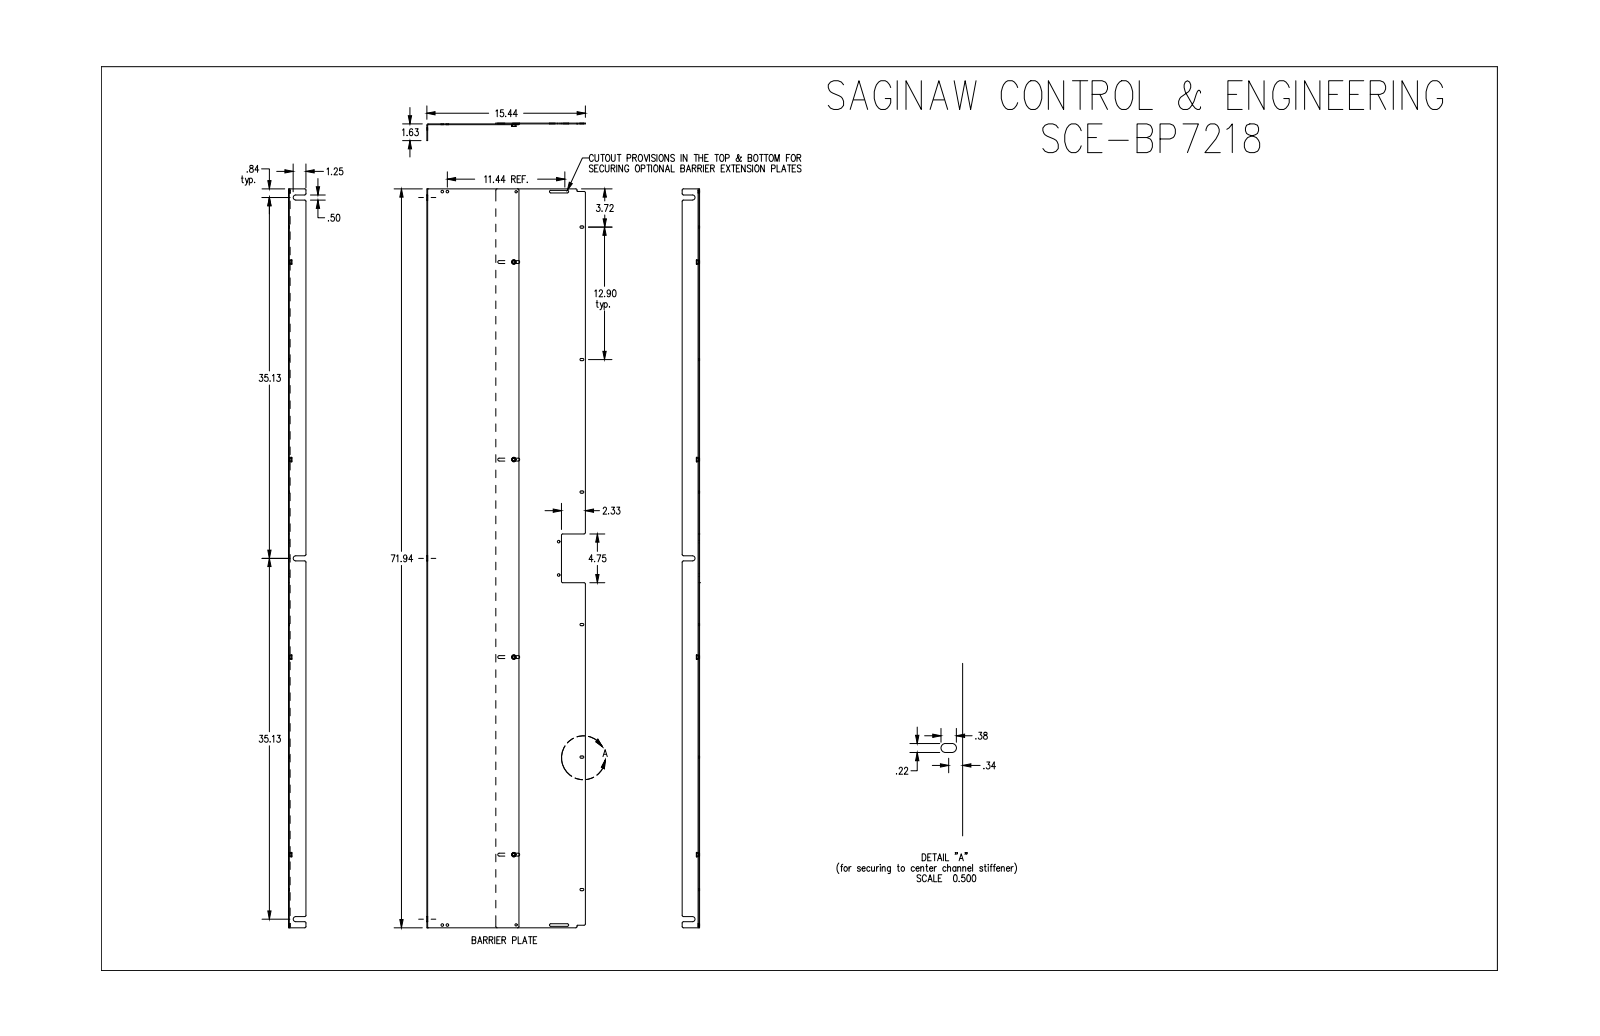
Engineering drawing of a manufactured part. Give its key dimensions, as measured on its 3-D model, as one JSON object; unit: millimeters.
{"part_name": "SCE-BP7218", "step_written_by": "SolidWorks 2019 (CONFIG_CONTROL_DESIGN)", "units": "millimeters", "bodies": {"solids": 6, "faces": 154, "planar": 67, "cylindrical": 75, "other": 12}, "overall_size": [1827.2, 392.2, 43.2], "volume_mm3": 1678000, "surface_area_mm2": 1780000, "round_holes": [[6.4, 10], [8.7, 4], [5.5, 2]], "round_bosses_or_shafts": [[11.2, 4], [8.7, 4]], "partial_cylinders_radius": [[3.2, 24], [2.8, 12], [3.6, 8], [6.4, 3], [1.6, 2], [1.1, 1], [3, 1]], "face_to_face_distances": [1.9, 3.8, 170.7, 168.8, 227.8, 225.9, 57.2, 43.2, 41.3, 39.4], "hole_center_spacings": [488.4, 12.7, 169.9, 173.9, 182.6, 231.3, 239.4, 248.3]}
